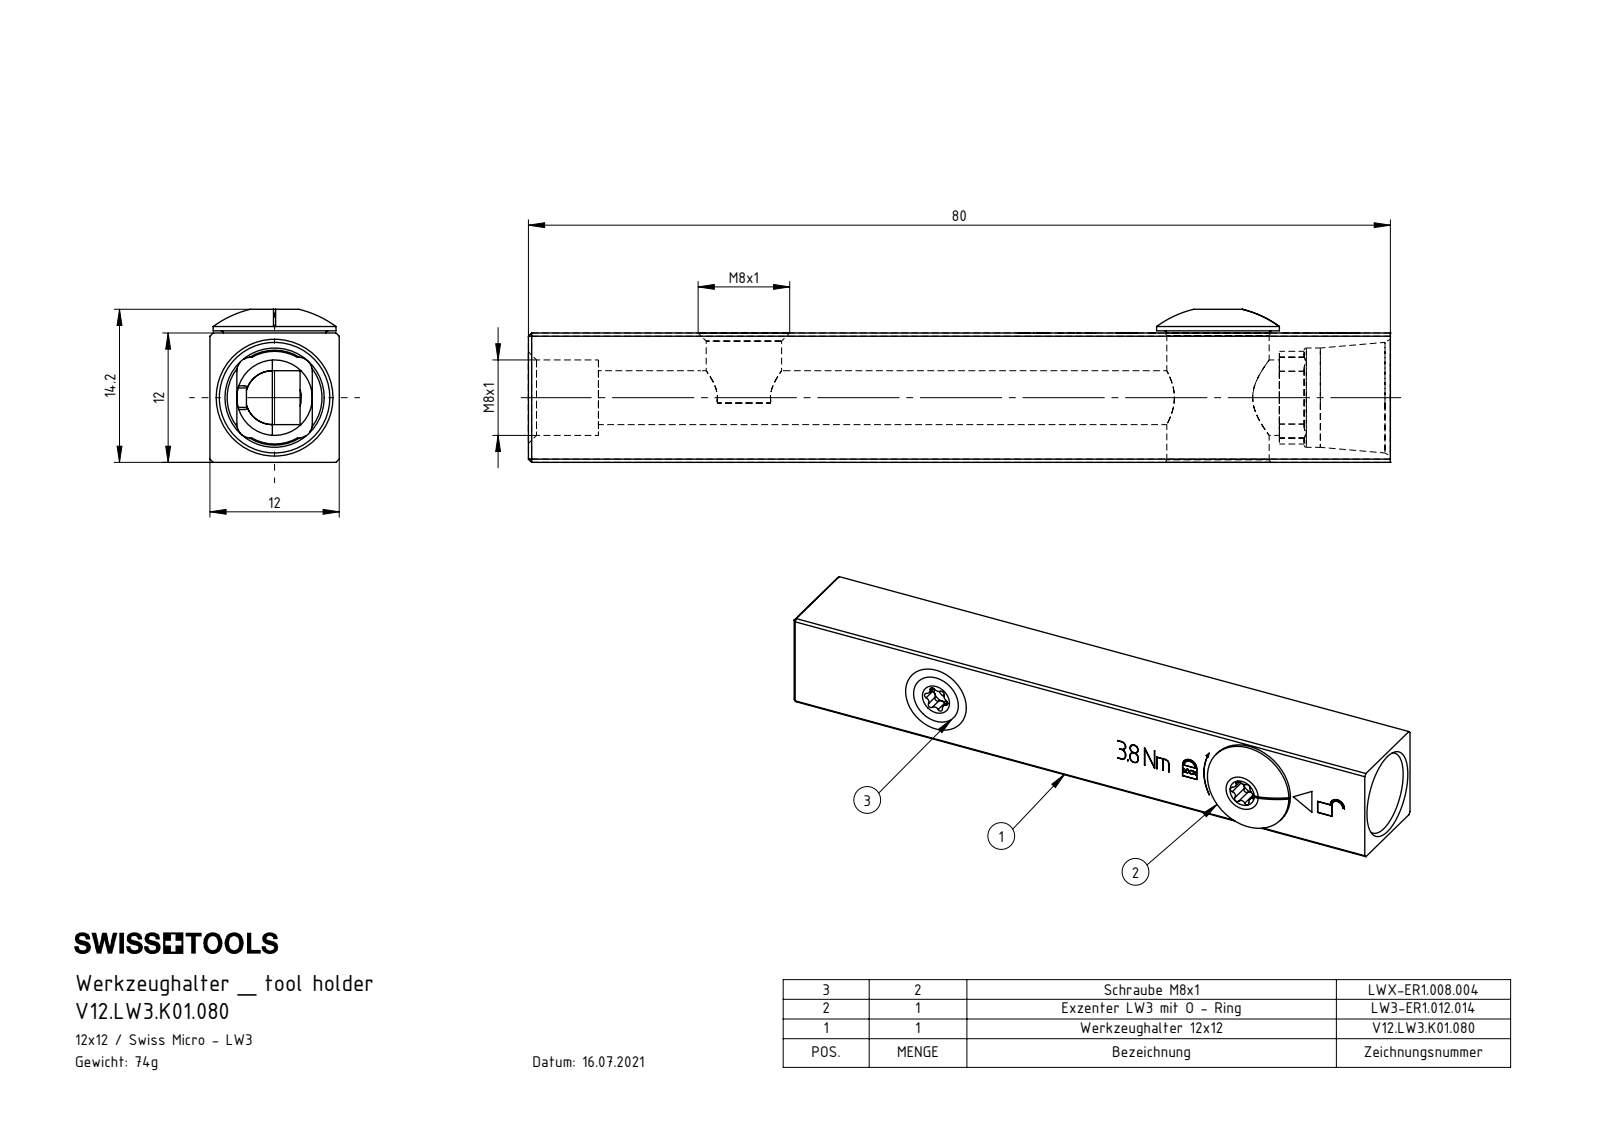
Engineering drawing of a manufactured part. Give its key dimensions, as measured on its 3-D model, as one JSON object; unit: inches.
{"part_name": "V12.LW3.K01.080; DIN 3771 - 7x1; LWX-ER1.008.004_A; V12-LW3.K01.080_D (+2 more)", "step_written_by": "SolidWorks 2022 (AUTOMOTIVE_DESIGN)", "units": "inches", "bodies": {"solids": 6, "faces": 200, "planar": 95, "cylindrical": 71, "other": 34}, "overall_size": [3.15, 0.559, 0.472], "volume_in3": 0.574, "surface_area_in2": 10.58, "round_holes": [[0.094, 3], [0.276, 2], [0.039, 1], [0.197, 1], [0.363, 1]], "round_bosses_or_shafts": [[0.315, 2], [0.449, 1], [0.374, 1], [0.303, 1]], "partial_cylinders_radius": [[0.013, 12], [0.023, 12], [0.013, 6], [0.023, 6], [0.051, 4], [0.098, 2], [0.142, 1], [0.146, 1]], "face_to_face_distances": [0.472, 0.079, 0.043, 0.016, 0.299, 0.157, 0.651, 0.457, 0.098, 0.315], "hole_center_spacings": [1.732]}
